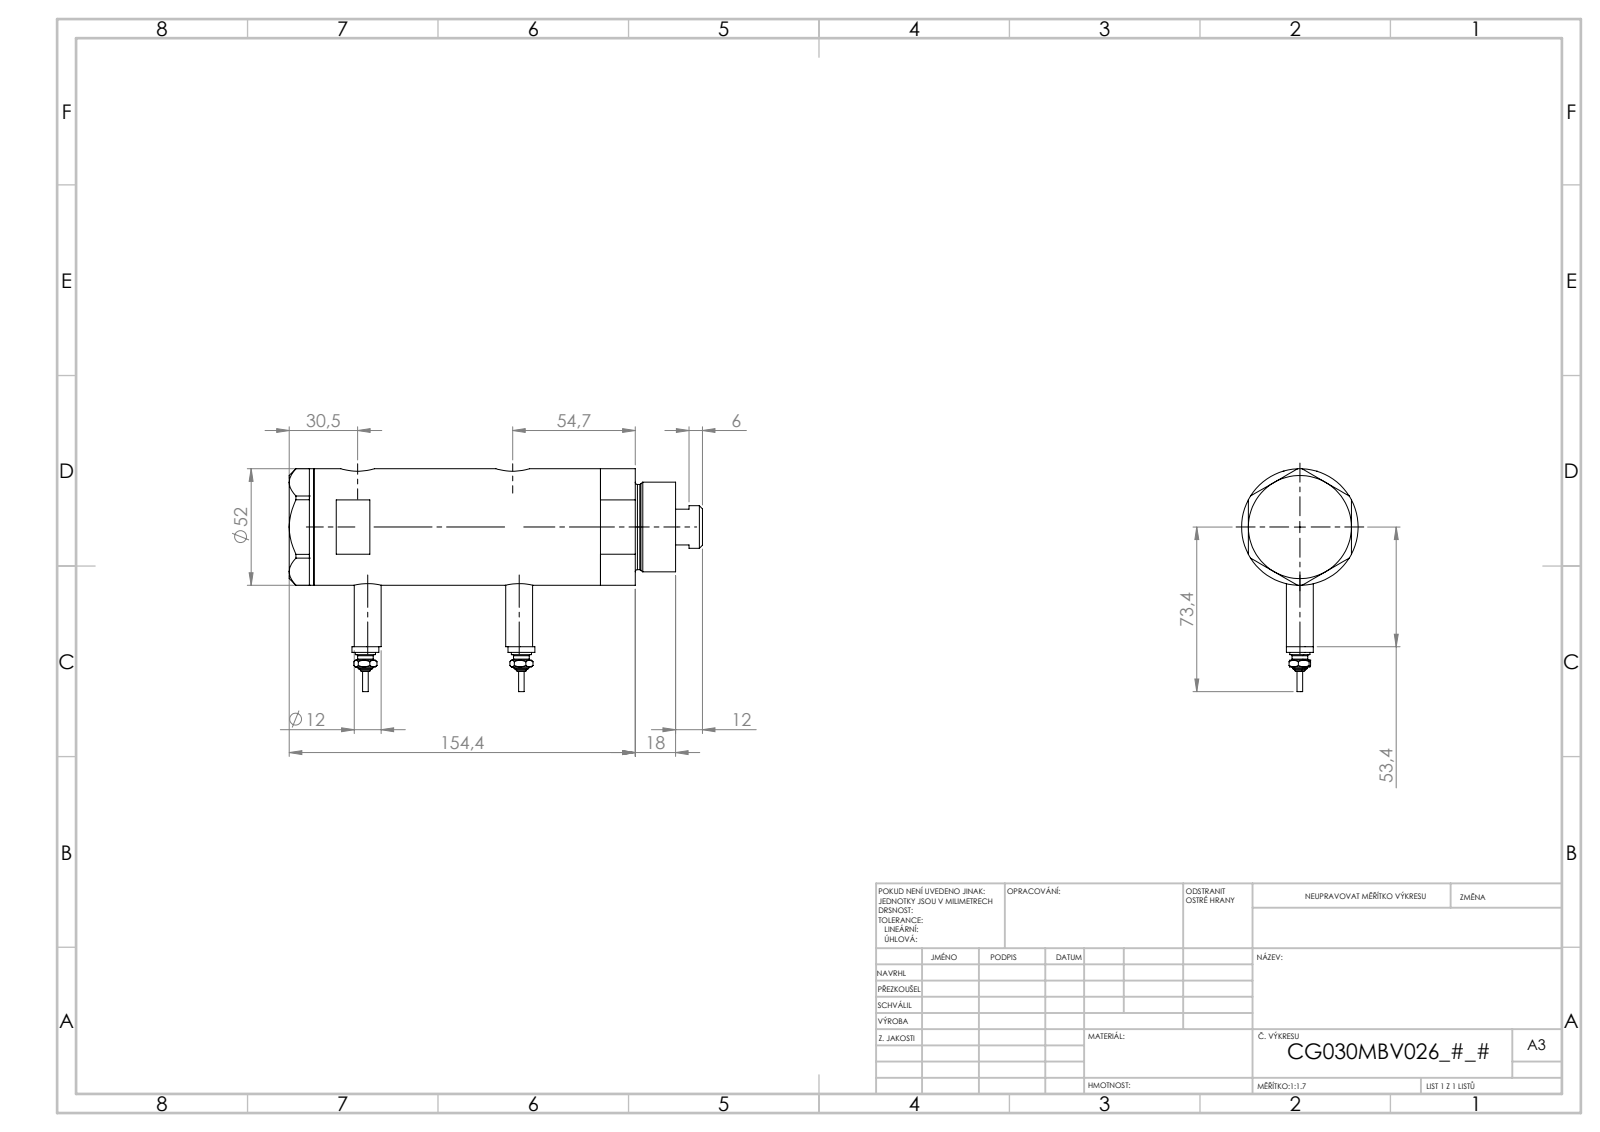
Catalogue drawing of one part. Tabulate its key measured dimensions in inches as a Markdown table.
| quantity | value |
| --- | --- |
| part name | V270CG_BACK; V270CG_VC; V270CG_FRONT; V270CG_MIDDLE (+1 more) |
| STEP written by | SolidWorks 2019 (CONFIG_CONTROL_DESIGN) |
| units | inches |
| bodies | 6 solids, 226 faces (93 planar, 69 cylindrical, 64 other) |
| overall size | 7.26 × 3.913 × 2.047 |
| volume | 20.9 in³ |
| surface area | 124.1 in² |
| round holes (diameter × count) | 0.383 × 2, 0.492 × 2, 0.591 × 2, 0.256 × 1, 0.787 × 1, 0.846 × 1, 1.181 × 1, 1.299 × 1, 1.732 × 1 |
| round bosses / shafts (diameter × count) | 0.472 × 4, 0.354 × 2, 0.276 × 2, 0.177 × 2, 0.098 × 2, 2.047 × 1, 1.575 × 1, 1.496 × 1 |
| main face-to-face distances | 3.602, 0.937, 2.665, 0.433, 1.37, 4.035, 1.811, 1.433, 5.469, 5.035 |
| hole center spacings | 0.114, 0.177, 2.547, 2.661, 2.724, 2.839 |
